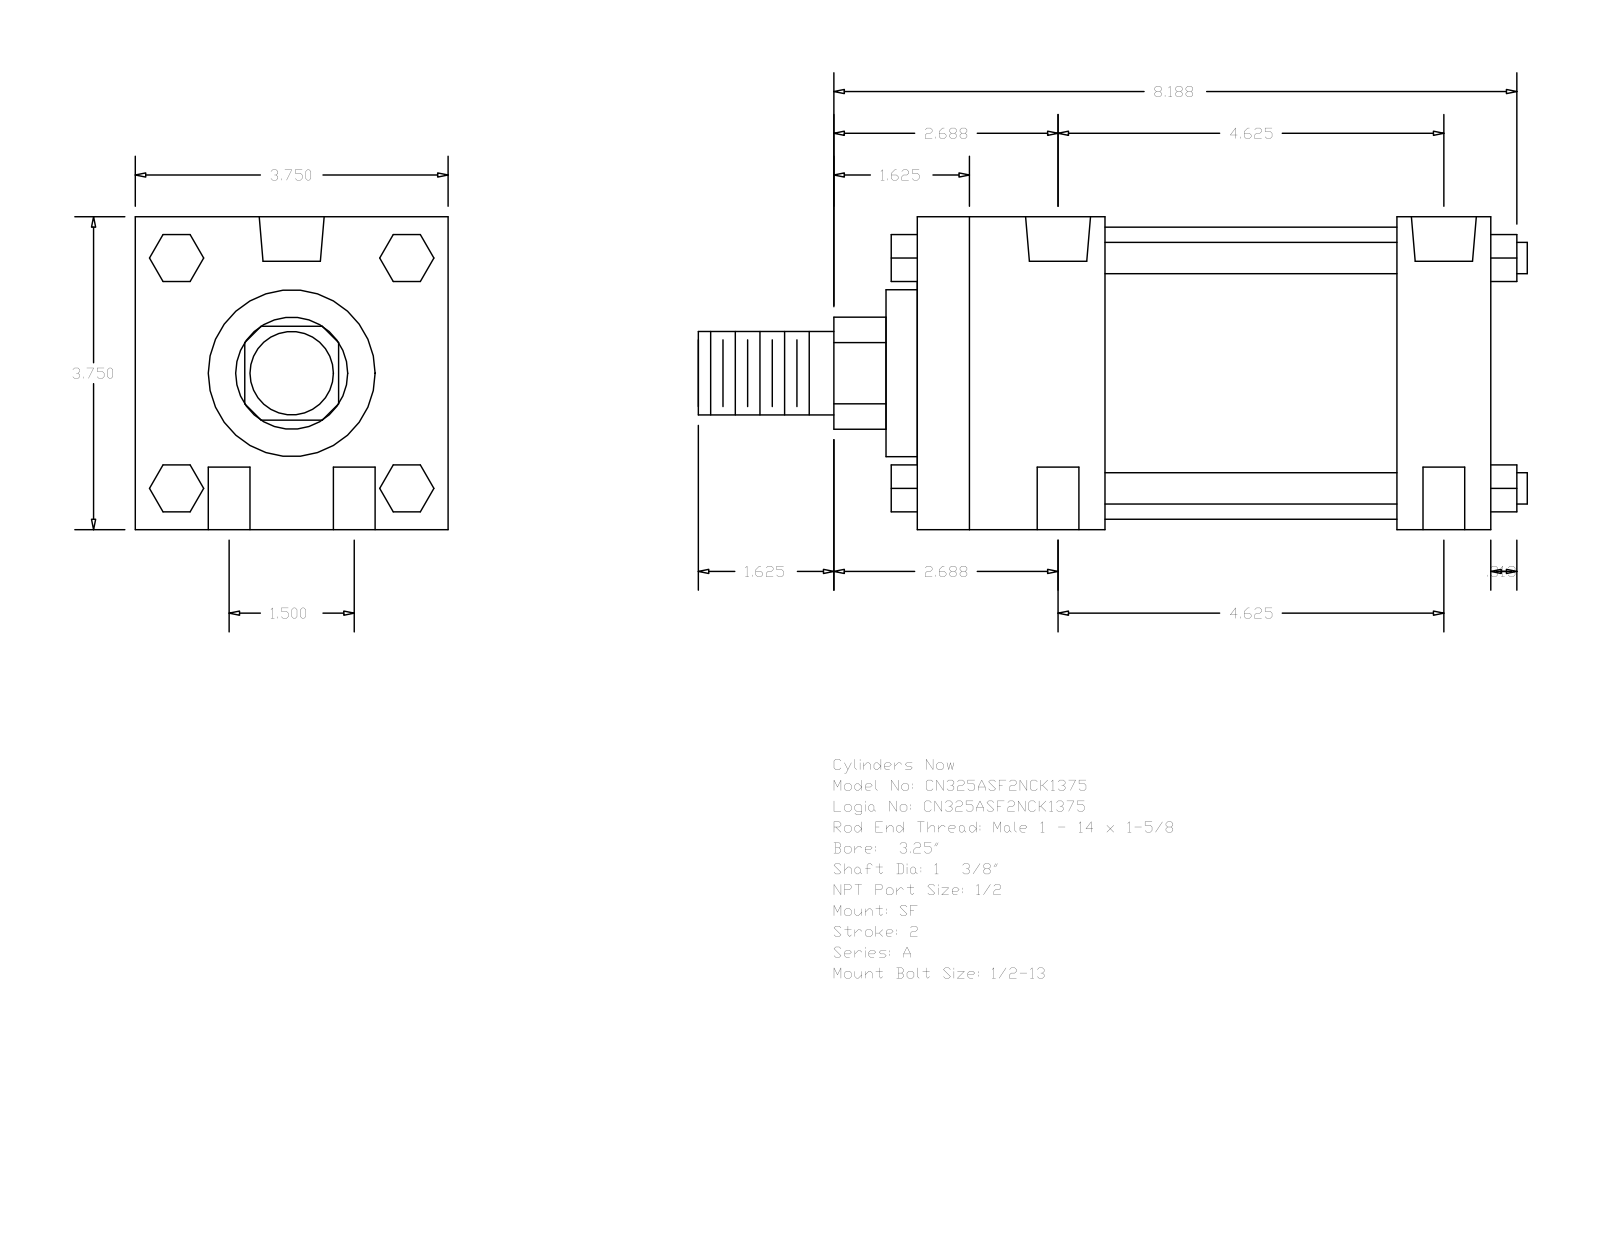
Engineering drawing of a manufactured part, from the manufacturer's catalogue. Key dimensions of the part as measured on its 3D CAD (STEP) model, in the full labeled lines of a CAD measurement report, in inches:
Part name (STEP PRODUCT): A_SF__0325_1.375
STEP written by: GSSL Pune (CONFIG_CONTROL_DESIGN)
Units: inches
Bodies: 0 solids, 124 faces (94 planar, 30 cylindrical, 0 other)
Overall size (bounding box): 9.937 × 3.75 × 3.75
Round holes (diameter × count): ⌀0.5 ×4, ⌀0.344 ×2, ⌀0.778 ×2
Round bosses / shafts (diameter × count): ⌀0.375 ×4, ⌀3.5 ×1, ⌀2 ×1, ⌀1.375 ×1, ⌀1 ×1
Partial cylindrical surfaces — rounded edges, fillets, slot ends (radius × count): R0.672 ×1
Main face-to-face distances: 3.75, 6.875, 2.25, 1.125, 5.75, 3.5, 4.625, 2.625, 0.375, 6.125
Hole centre spacings: 0.75, 4.685, 4.625, 1.5, 4.862, 4.375
